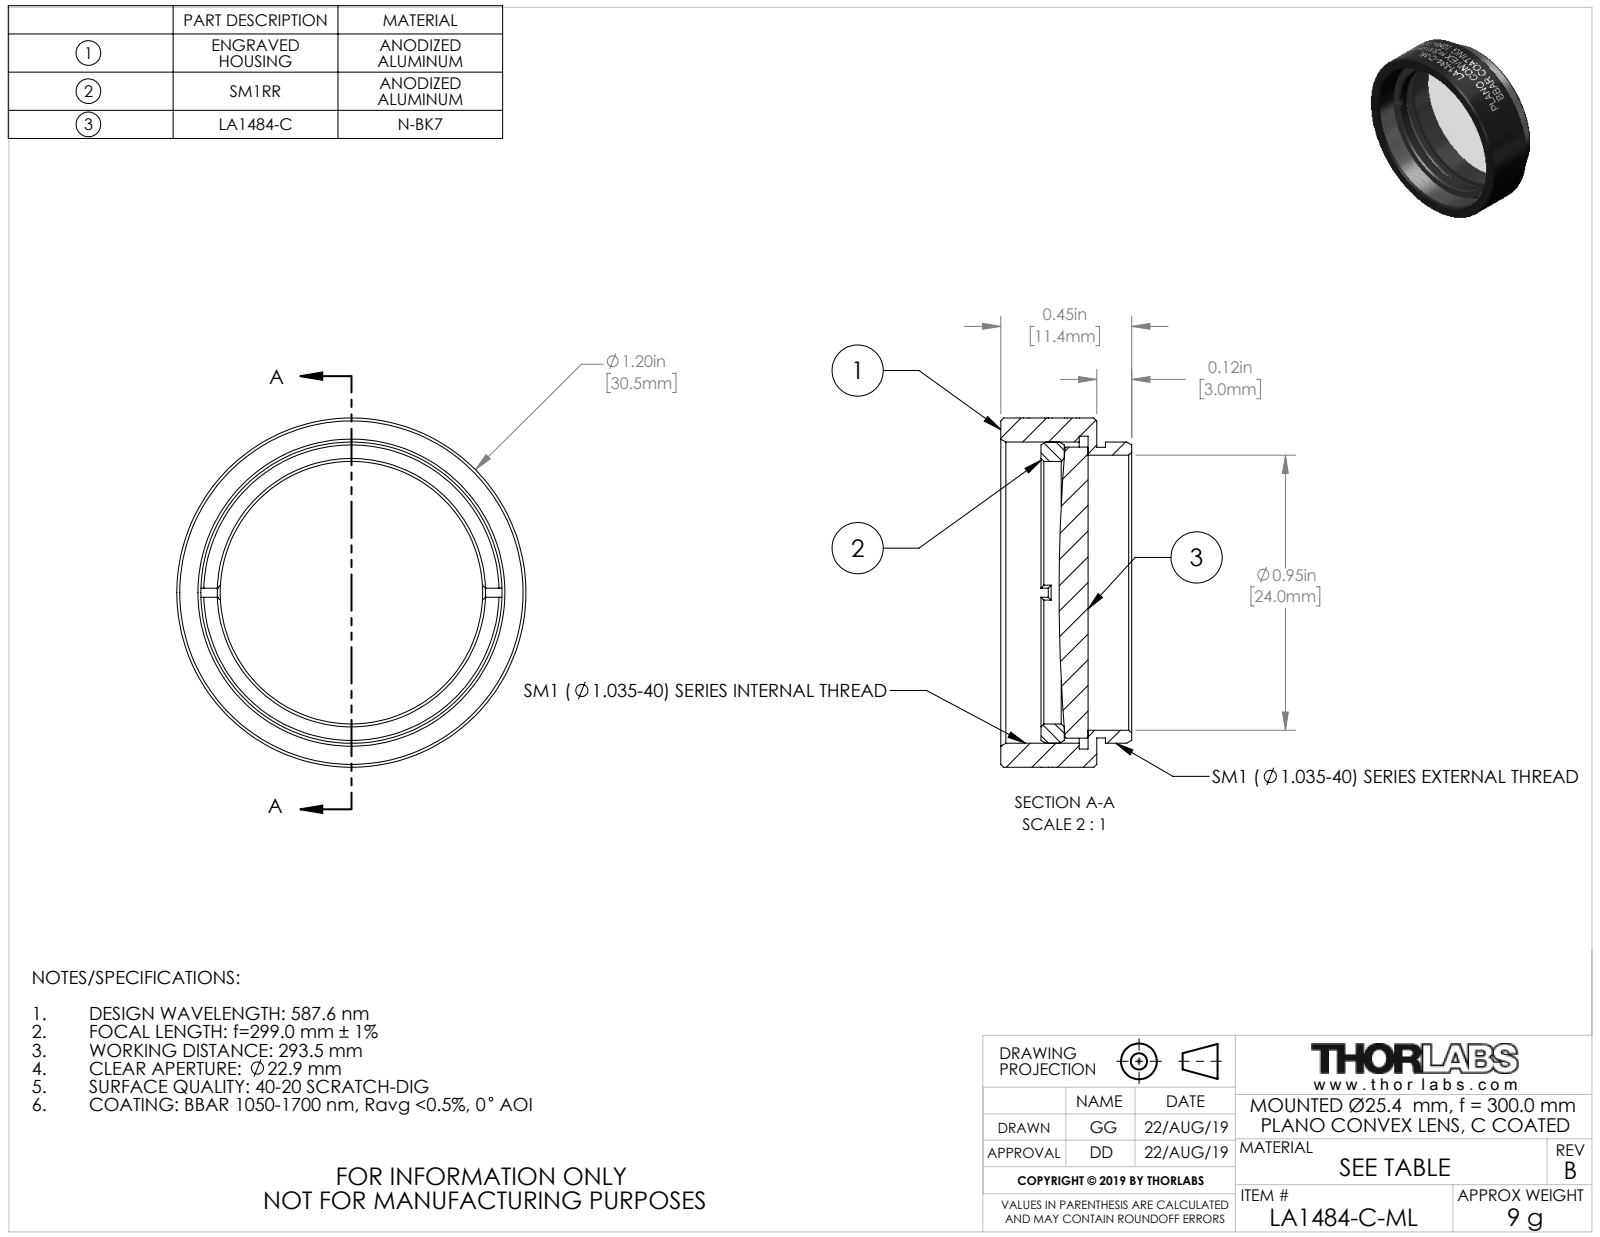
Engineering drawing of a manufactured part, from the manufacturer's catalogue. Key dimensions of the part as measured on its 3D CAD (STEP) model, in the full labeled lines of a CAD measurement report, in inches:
Part name (STEP PRODUCT): 24425-E0W
STEP written by: SolidWorks 2018 (CONFIG_CONTROL_DESIGN)
Units: inches
Bodies: 3 solids, 161 faces (20 planar, 113 cylindrical, 28 other)
Overall size (bounding box): 1.2 × 1.2 × 0.45
Volume: 0.197 in³ · Surface area: 6.676 in²
Round holes (diameter × count): ⌀0.902 ×1, ⌀0.945 ×1, ⌀1.035 ×1, ⌀1.075 ×1
Round bosses / shafts (diameter × count): ⌀1.2 ×1, ⌀1.035 ×1, ⌀1 ×1, ⌀0.999 ×1
Main face-to-face distances: 0.03, 0.33, 0.3, 0.112, 0.082, 0.218, 0.192, 0.162, 0.08, 0.138
